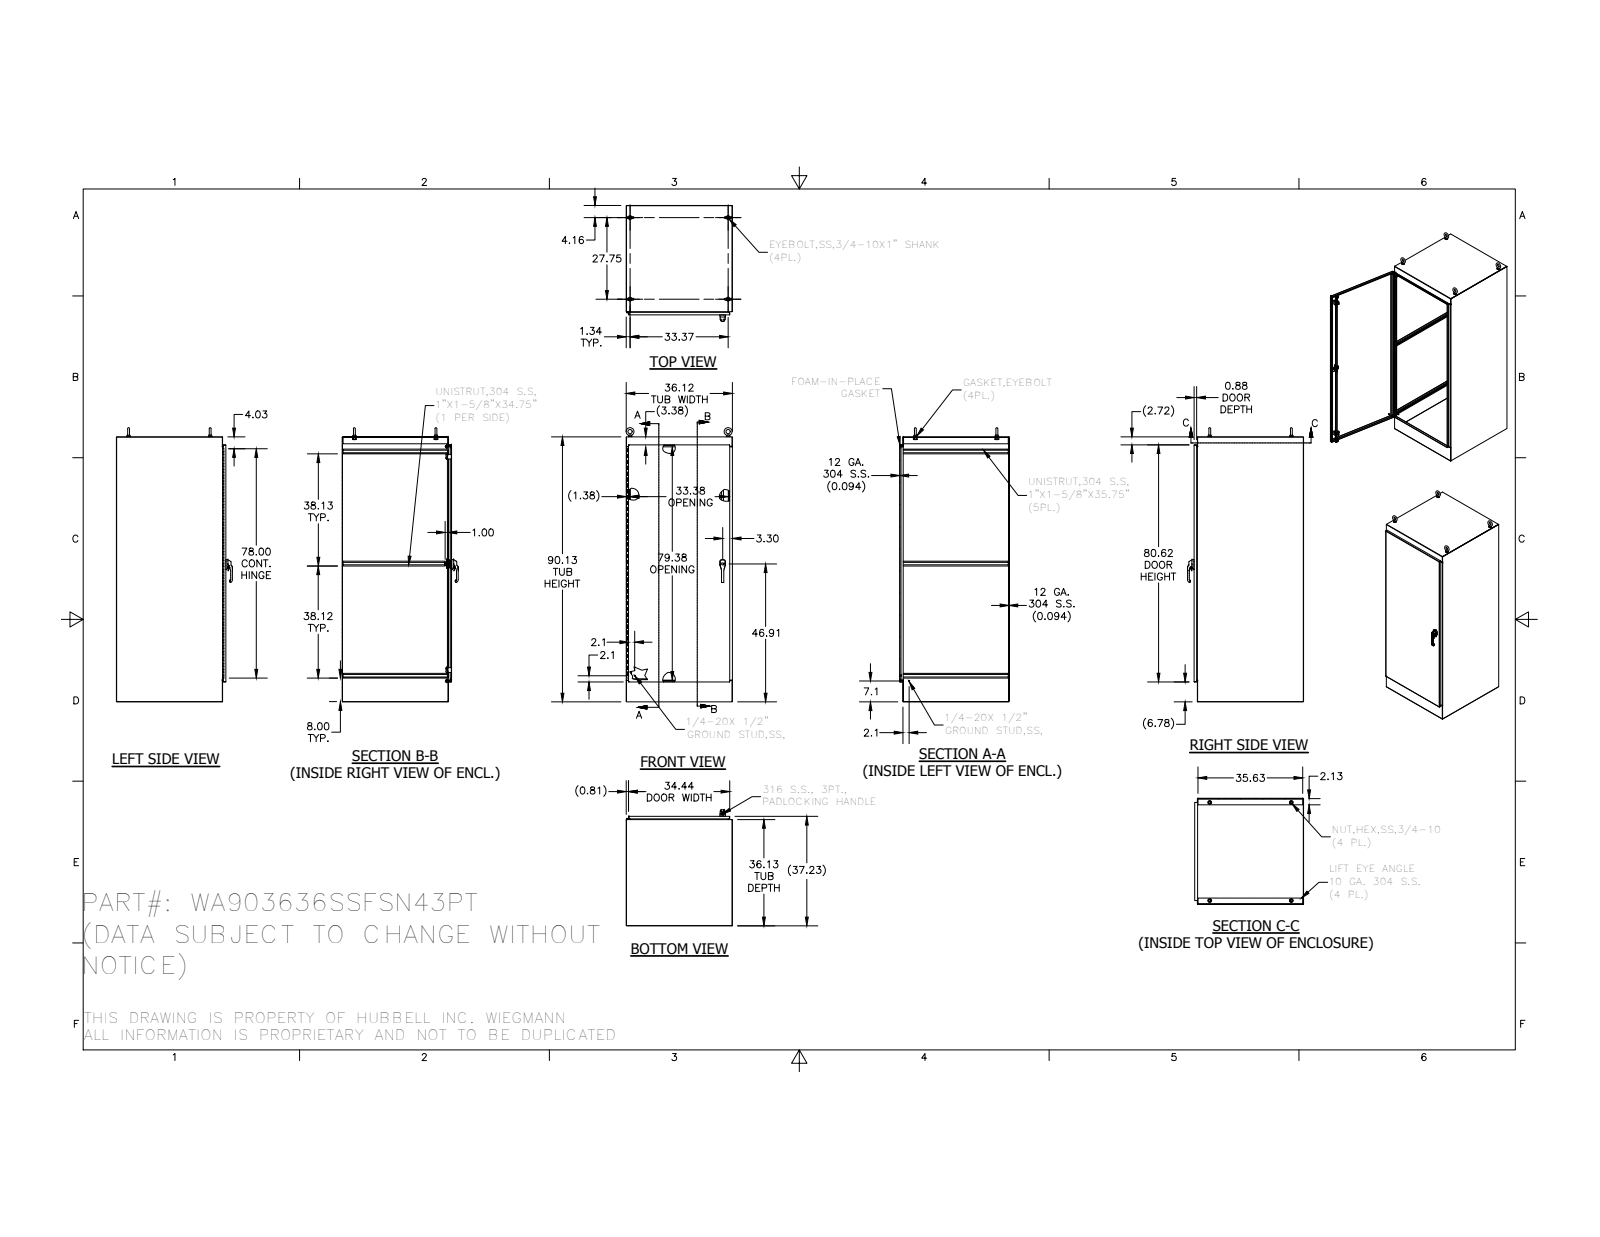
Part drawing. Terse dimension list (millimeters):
name: 1091-903_AF0_2; 31230; 37031; HFW3762 (+8 more)
written by: SolidWorks 2014 (AUTOMOTIVE_DESIGN)
unit: mm
bodies: 72 solids, 3897 faces (1333 planar, 1416 cylindrical, 1148 other)
size: 2368.5 × 1002.7 × 917.6
volume: 28 420 000 mm³; area: 23 260 000 mm²
holes: 8× ⌀6.7, 8× ⌀9.5, 4× ⌀4.7, 4× ⌀16.3, 4× ⌀20.7, 4× ⌀20.7, 3× ⌀5.4, 3× ⌀6.4, 3× ⌀7.1, 2× ⌀4.2, 2× ⌀6.1, 2× ⌀6.4
bosses: 4× ⌀31.8, 4× ⌀28.4, 4× ⌀19.1, 3× ⌀25.4, 3× ⌀6, 2× ⌀14.3, 2× ⌀13.5, 2× ⌀13.5
rounds: 180× R0.5, 107× R0.3, 26× R3.2, 23× R0.5, 19× R1.3, 17× R0.8, 14× R2, 13× R3.2
face distances: 2.4, 915.2, 943.2, 912.8, 917.6, 940.8, 945.6, 2286.8, 2284.4, 2289.2
hole spacings: 849.3, 220.1, 660.4, 9.7, 19.3, 28, 43.5, 70.2
